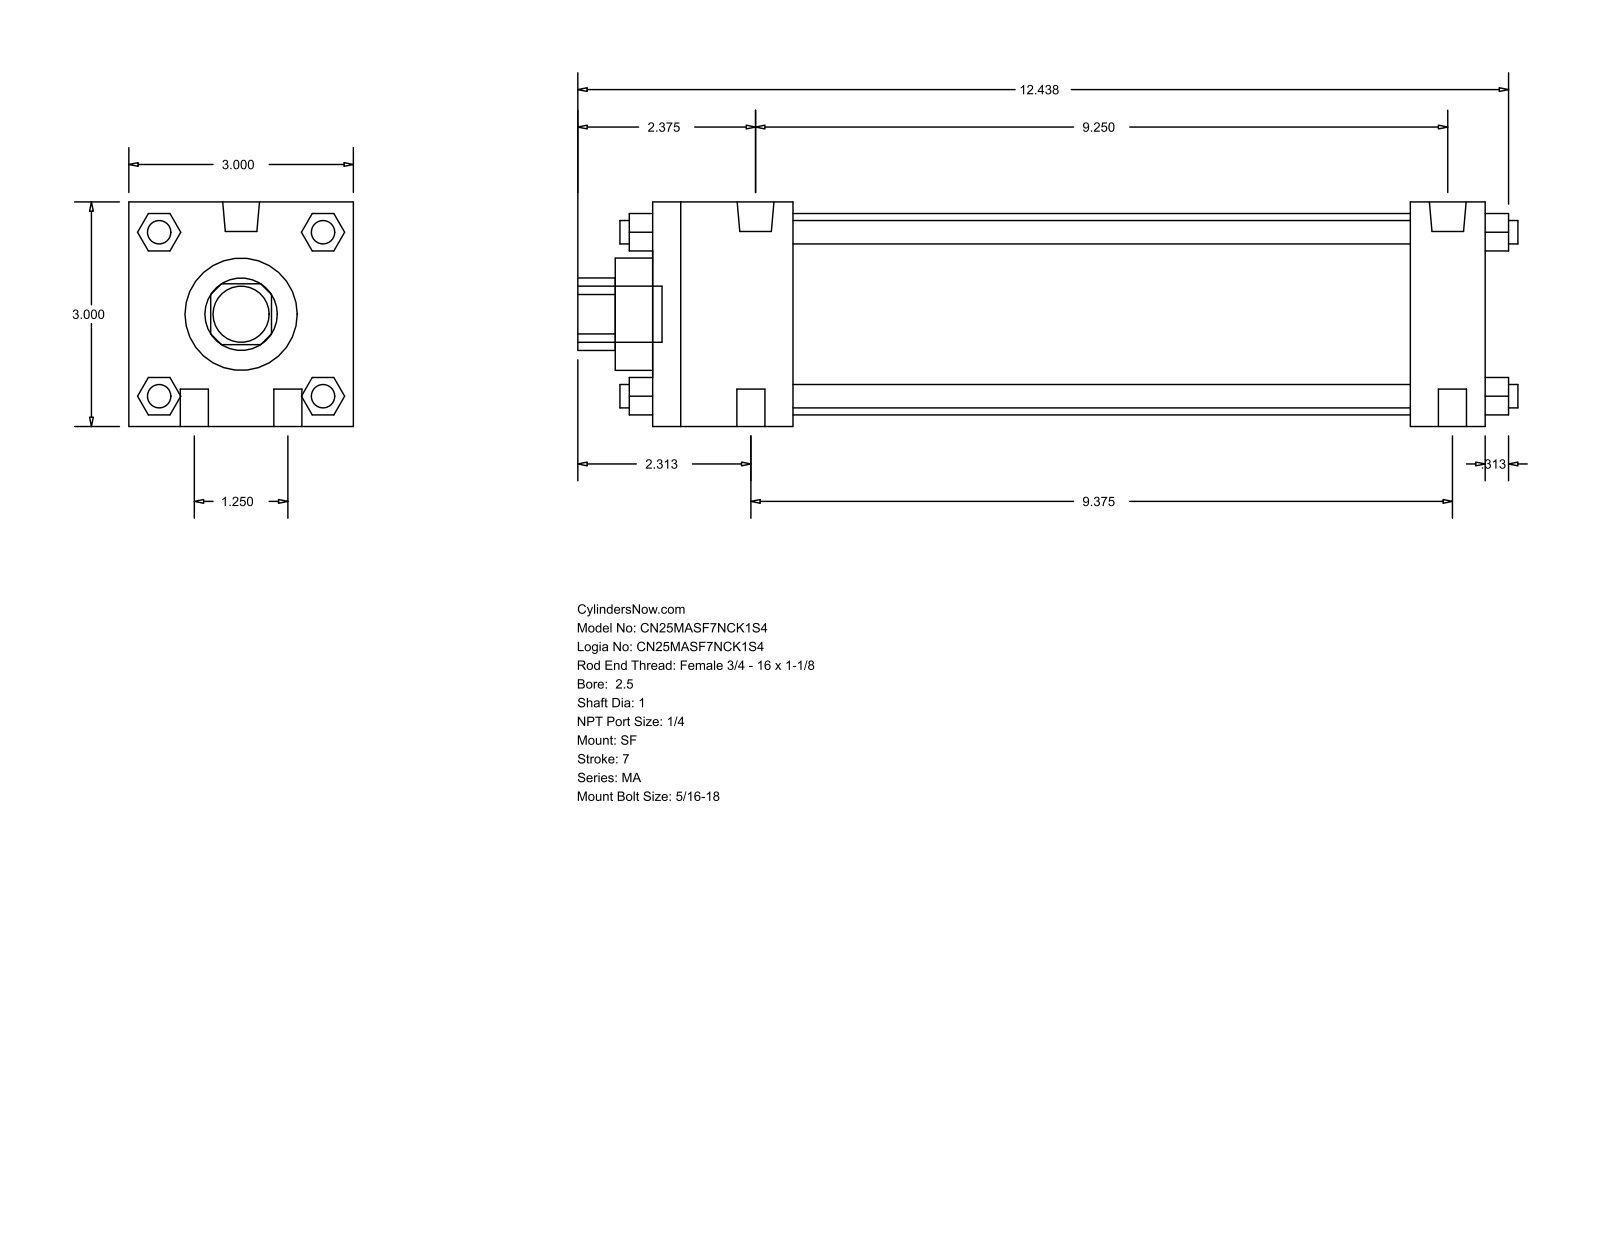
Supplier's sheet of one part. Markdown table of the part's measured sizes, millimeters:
| quantity | value |
| --- | --- |
| part name | MA_SF__0250_1 |
| STEP written by | GSSL Pune (CONFIG_CONTROL_DESIGN) |
| units | millimeters |
| bodies | 0 solids, 124 faces (94 planar, 30 cylindrical, 0 other) |
| overall size | 319.09 × 76.2 × 76.2 |
| round holes (diameter × count) | 25.4 × 1, 38.1 × 1, 68.33 × 1 |
| round bosses / shafts (diameter × count) | 7.94 × 6, 9.53 × 4, 12.49 × 2, 19.05 × 1 |
| partial cylindrical surfaces (radius × count) | 12.29 × 1 |
| main face-to-face distances | 76.2, 282.58, 12.7, 257.17, 25.41, 47.63, 209.54, 234.95, 27.81, 48.17 |
